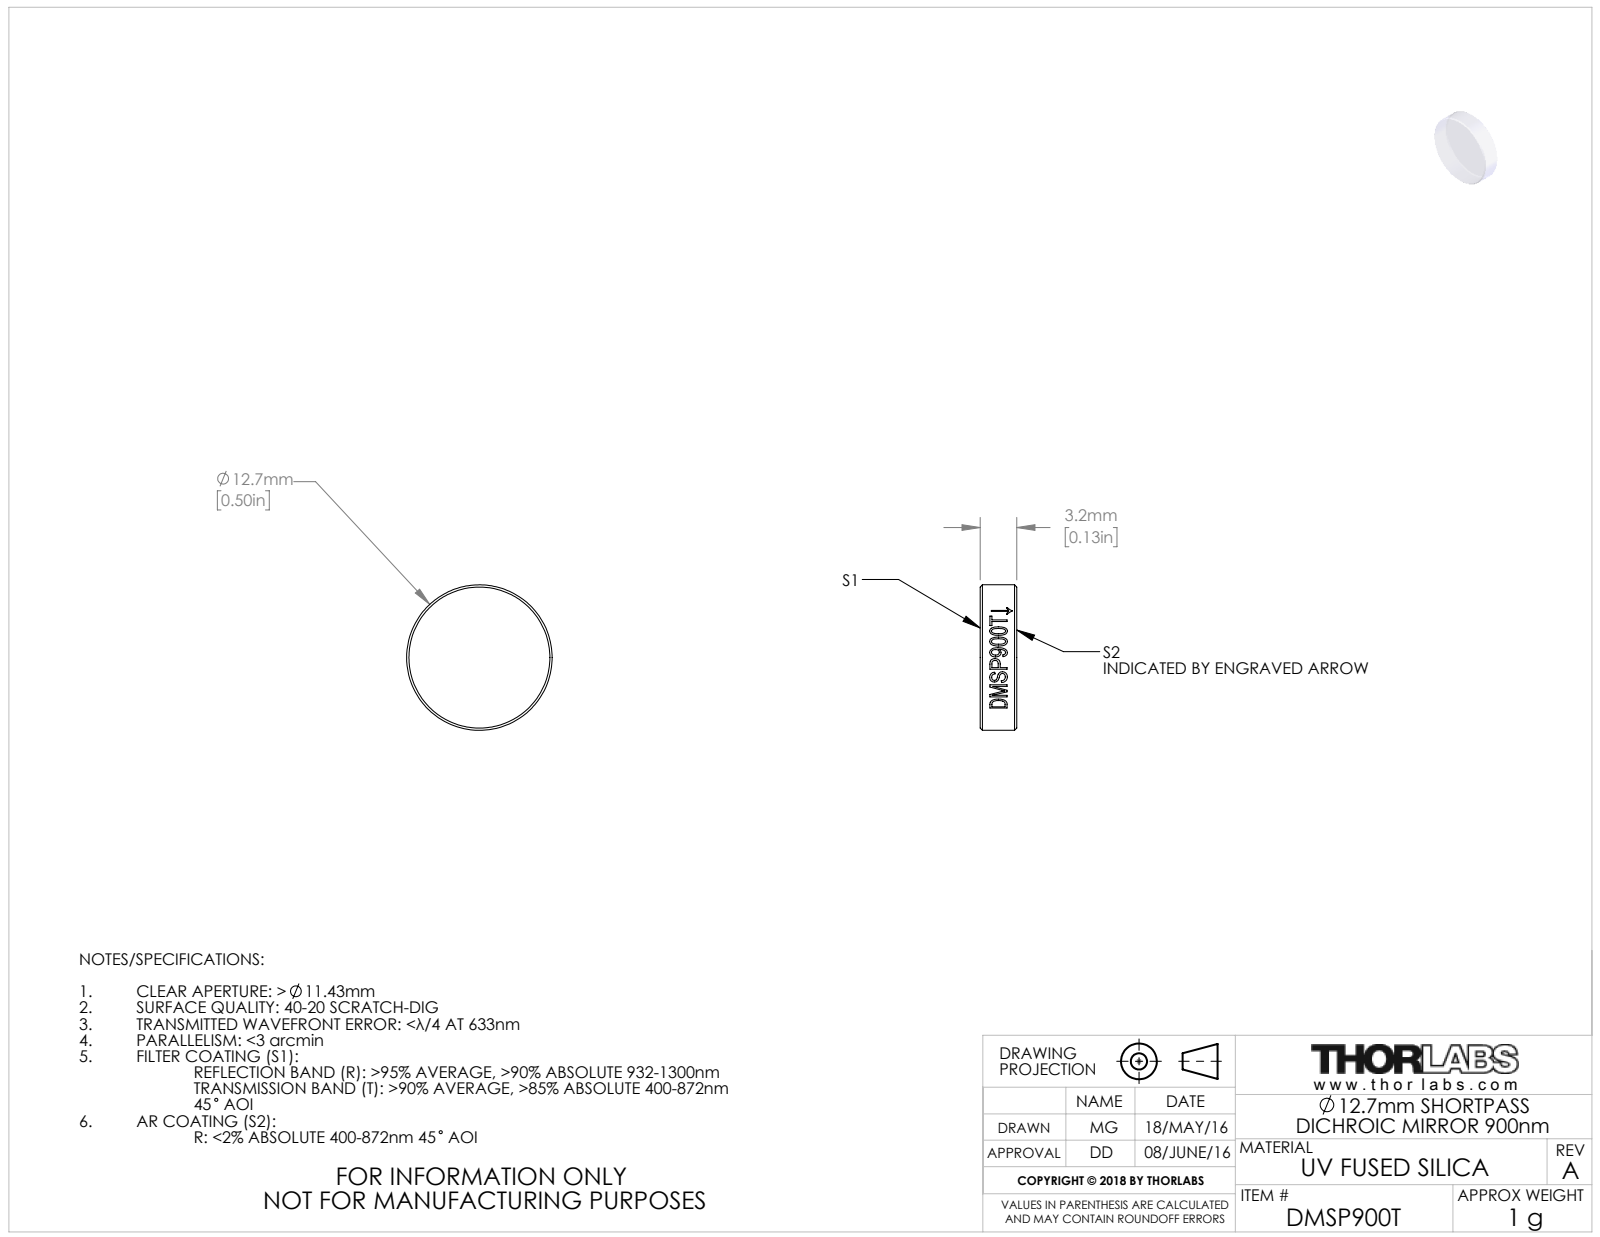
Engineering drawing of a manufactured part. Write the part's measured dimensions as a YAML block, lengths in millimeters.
part_name: "TTN045292-E0W"
step_written_by: "SolidWorks 2016 (CONFIG_CONTROL_DESIGN)"
units: millimeters
bodies: {solids: 1, faces: 22, planar: 2, cylindrical: 16, other: 4}
overall_size: [12.7, 12.7, 3.2]
volume: 404
surface_area: 372
round_bosses_or_shafts:
  - {diameter: 12.7, count: 1}
face_to_face_distances: [3.2]
